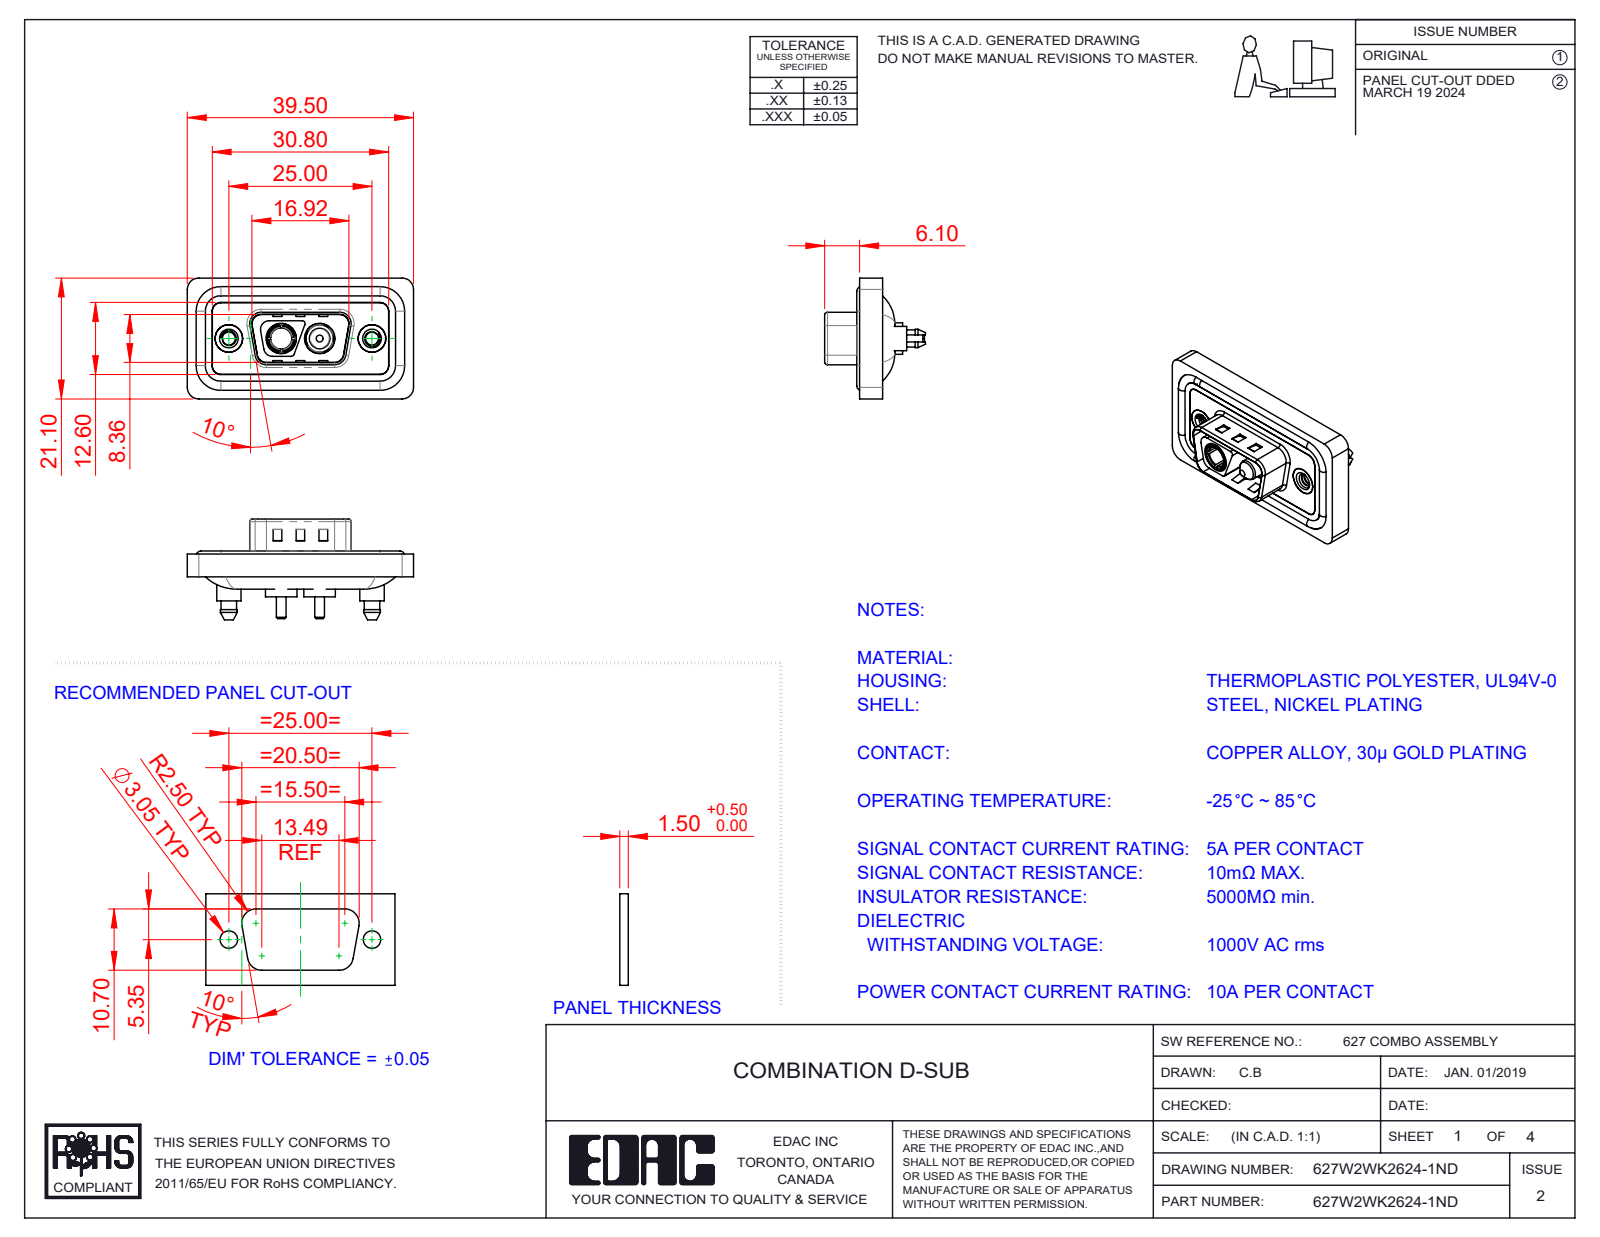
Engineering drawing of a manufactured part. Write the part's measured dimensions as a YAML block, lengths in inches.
part_name: "627Combo Shell Front_09 Contacts; Power Socket_10A S; 627Combo Shell Rear_09 Contacts; Power Pin_10A S (+5 more)"
step_written_by: "SolidWorks 2023 (CONFIG_CONTROL_DESIGN)"
units: inches
bodies: {solids: 11, faces: 592, planar: 205, cylindrical: 267, other: 120}
overall_size: [1.555, 0.831, 0.693]
volume: 0.284
surface_area: 11.86
round_holes:
  - {diameter: 0.089, count: 2}
  - {diameter: 0.157, count: 2}
  - {diameter: 0.189, count: 2}
  - {diameter: 0.191, count: 2}
  - {diameter: 0.197, count: 2}
  - {diameter: 0.209, count: 2}
  - {diameter: 0.146, count: 1}
round_bosses_or_shafts:
  - {diameter: 0.063, count: 4}
  - {diameter: 0.217, count: 2}
  - {diameter: 0.213, count: 2}
  - {diameter: 0.205, count: 2}
  - {diameter: 0.193, count: 2}
  - {diameter: 0.187, count: 2}
  - {diameter: 0.167, count: 2}
  - {diameter: 0.148, count: 2}
partial_cylinders:
  - {radius: 0.059, count: 26}
  - {radius: 0.079, count: 18}
  - {radius: 0.02, count: 10}
  - {radius: 0.063, count: 10}
  - {radius: 0.01, count: 4}
  - {radius: 0.024, count: 4}
  - {radius: 0.026, count: 4}
  - {radius: 0.035, count: 4}
face_to_face_distances: [0.016, 0.043, 0.114, 0.02, 0.063, 0.122, 0.059, 0.157, 0.071, 0.126]
hole_center_spacings: [0.36, 0.624, 0.265, 0.984]
